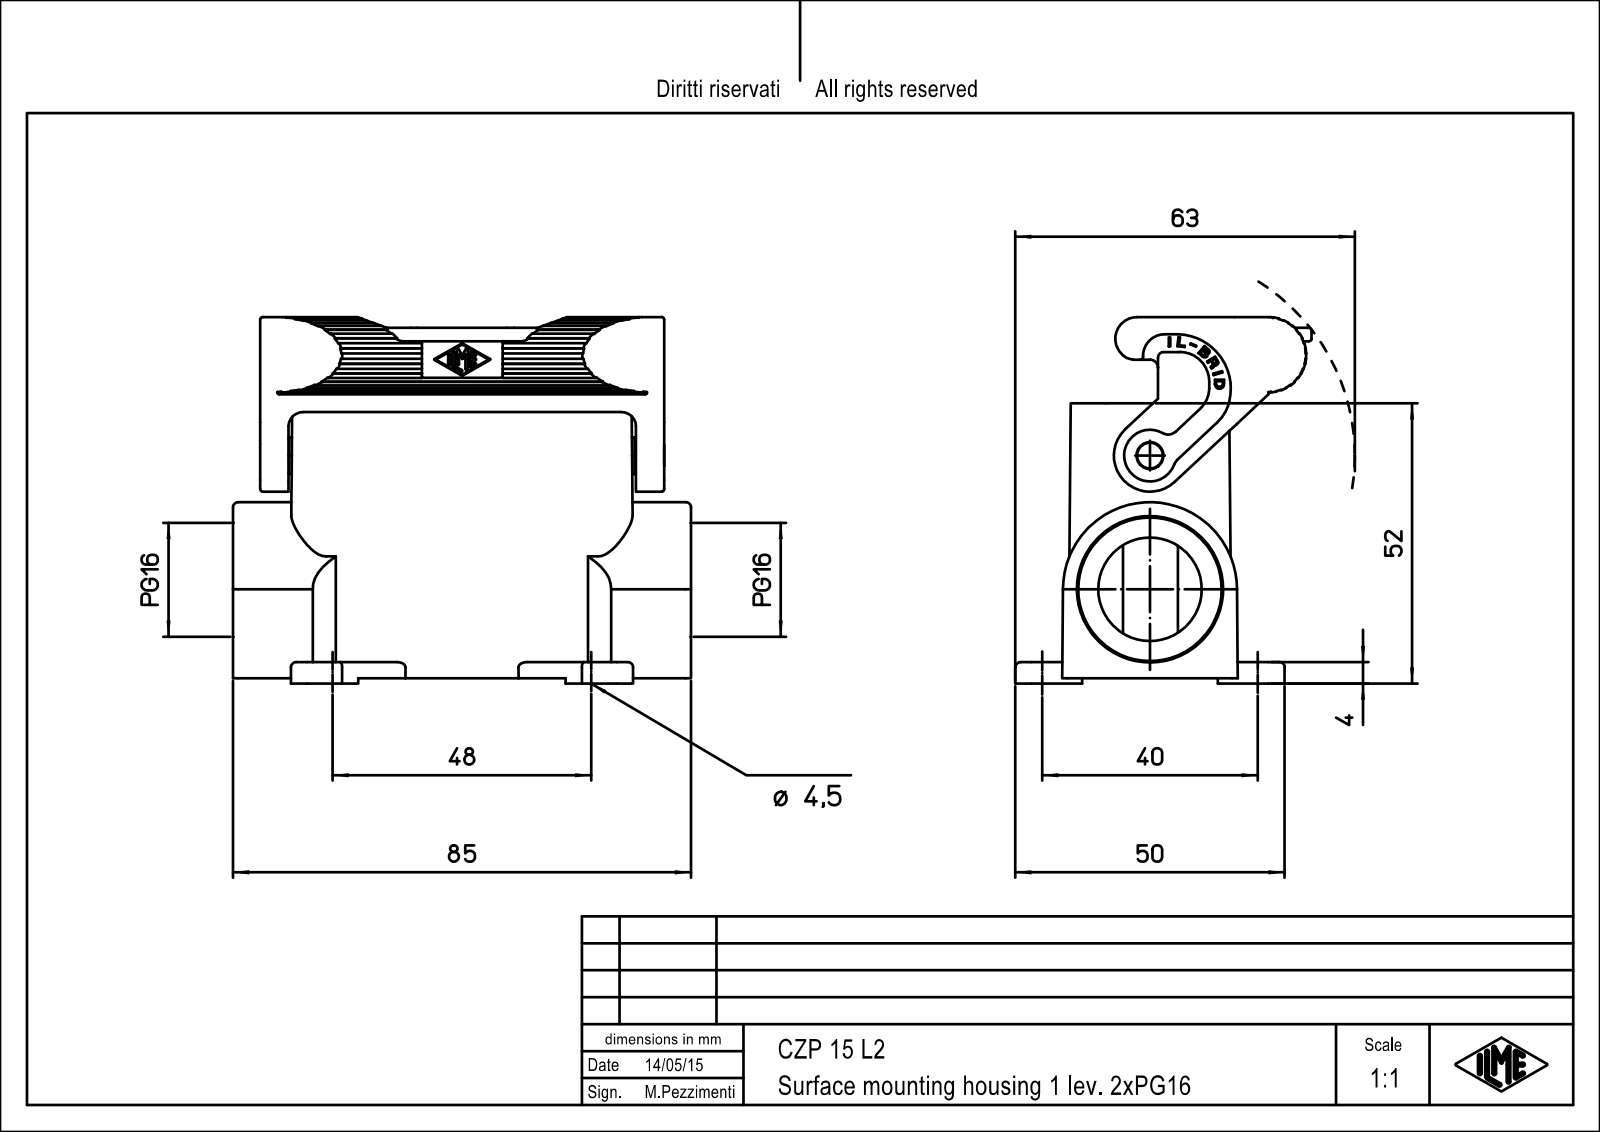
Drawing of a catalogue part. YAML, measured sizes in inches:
part_name: "CZ_MZ Gehäuse 1 Bügel"
step_written_by: "Autodesk Inventor 7 (AUTOMOTIVE_DESIGN)"
units: inches
bodies: {solids: 3, faces: 316, planar: 112, cylindrical: 78, other: 126}
overall_size: [3.346, 2.717, 2.122]
volume: 3.264
surface_area: 48.52
round_holes:
  - {diameter: 0.177, count: 2}
  - {diameter: 0.122, count: 1}
  - {diameter: 0.754, count: 1}
  - {diameter: 0.833, count: 1}
round_bosses_or_shafts:
  - {diameter: 0.394, count: 1}
  - {diameter: 0.248, count: 1}
  - {diameter: 0.197, count: 1}
  - {diameter: 0.102, count: 1}
  - {diameter: 0.098, count: 1}
partial_cylinders:
  - {radius: 0.015, count: 14}
  - {radius: 0.059, count: 6}
  - {radius: 0.118, count: 5}
  - {radius: 0.236, count: 5}
  - {radius: 0.039, count: 4}
  - {radius: 0.055, count: 3}
  - {radius: 0.11, count: 3}
  - {radius: 0.02, count: 2}
face_to_face_distances: [0.108, 1.073, 1.181, 0.965, 0.055, 0.138, 0.148, 0.039, 1.112, 1.22]
hole_center_spacings: [1.855, 2.459]
